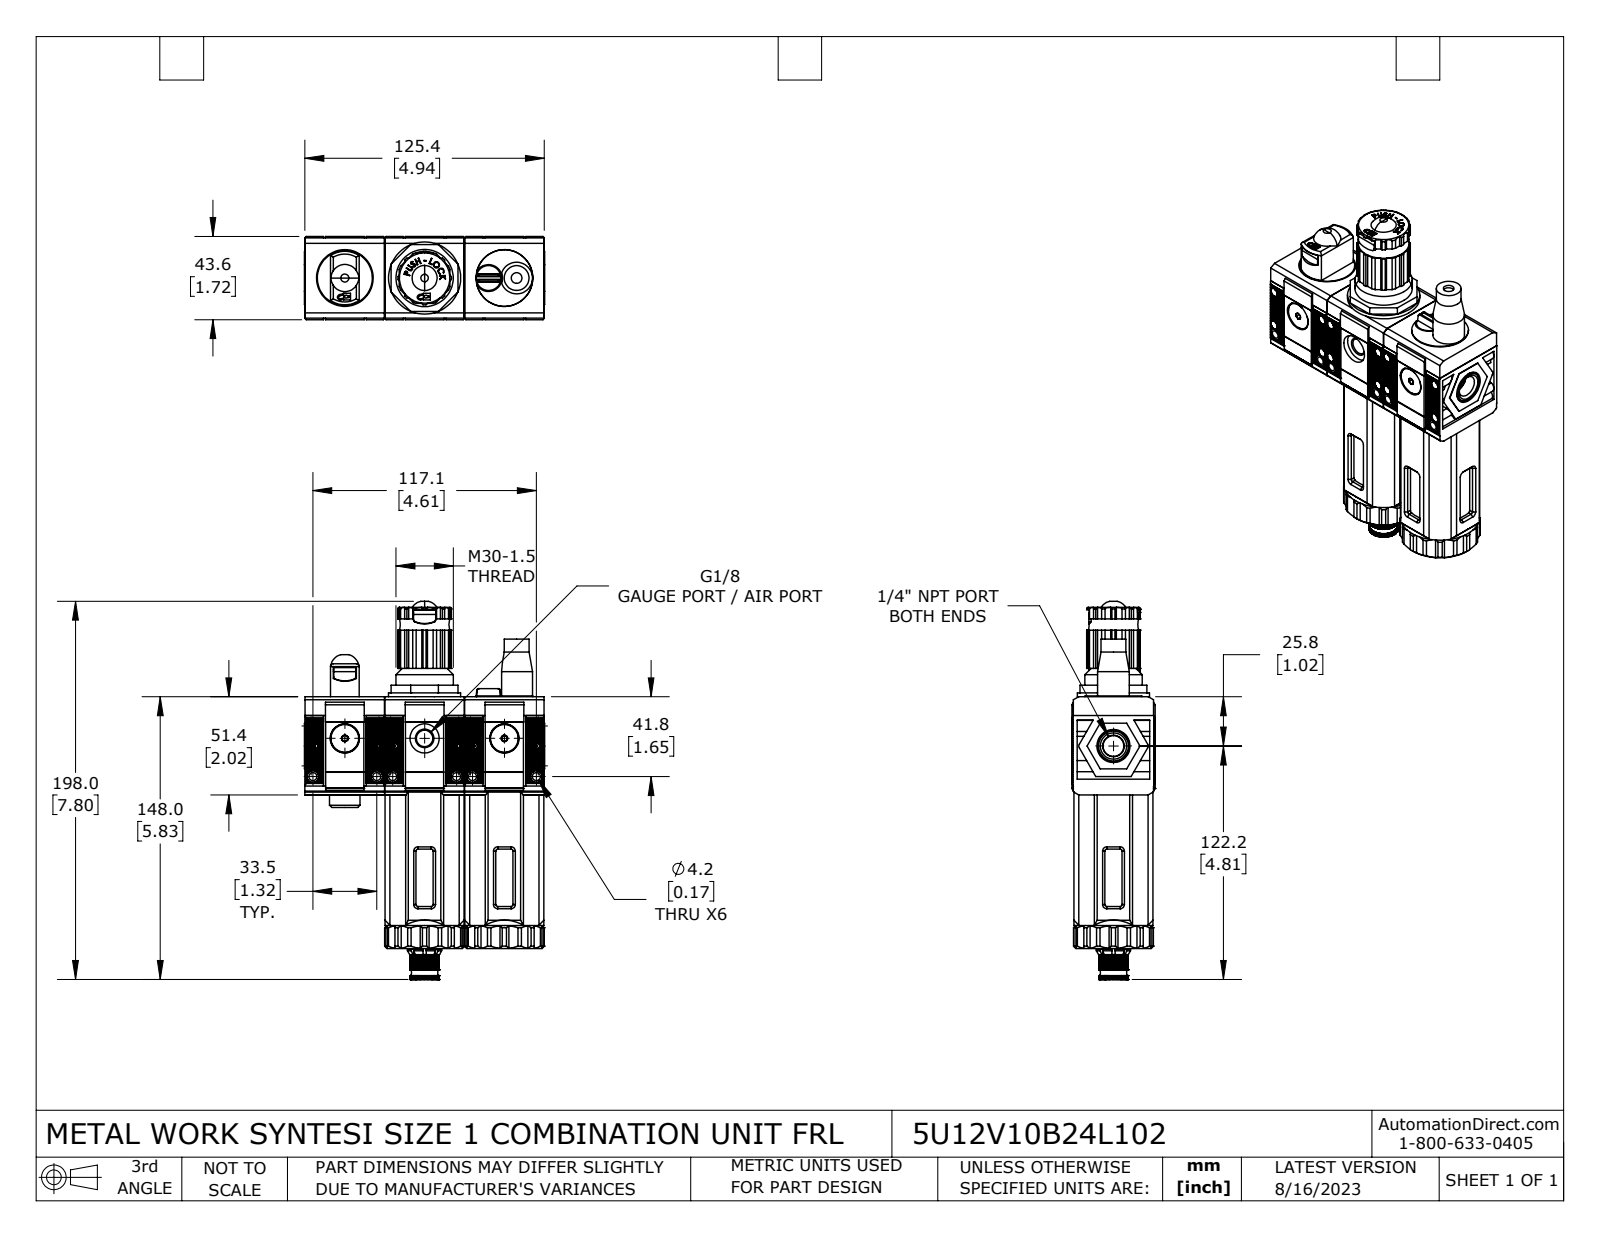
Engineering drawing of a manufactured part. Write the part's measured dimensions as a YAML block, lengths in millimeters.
part_name: "5U12V10B24L102"
step_written_by: "SolidWorks 2021 (CONFIG_CONTROL_DESIGN)"
units: millimeters
bodies: {solids: 40, faces: 4635, planar: 3330, cylindrical: 890, other: 415}
overall_size: [198, 125.8, 43.6]
volume: 388900
surface_area: 172600
round_holes:
  - {diameter: 2.1, count: 12}
  - {diameter: 3, count: 12}
  - {diameter: 4.7, count: 12}
  - {diameter: 4.2, count: 6}
  - {diameter: 8.6, count: 4}
  - {diameter: 15.3, count: 3}
  - {diameter: 3.5, count: 2}
  - {diameter: 29.7, count: 2}
  - {diameter: 30, count: 2}
  - {diameter: 31.3, count: 2}
  - {diameter: 34, count: 2}
  - {diameter: 35.4, count: 2}
round_bosses_or_shafts:
  - {diameter: 4.6, count: 12}
  - {diameter: 2.6, count: 12}
  - {diameter: 6.2, count: 6}
  - {diameter: 15, count: 3}
  - {diameter: 9.7, count: 3}
  - {diameter: 41.4, count: 2}
  - {diameter: 35.6, count: 2}
  - {diameter: 25, count: 2}
partial_cylinders:
  - {radius: 1, count: 14}
  - {radius: 3.1, count: 12}
  - {radius: 1.5, count: 7}
  - {radius: 0.6, count: 4}
  - {radius: 0.2, count: 2}
  - {radius: 0.5, count: 2}
  - {radius: 0.8, count: 2}
  - {radius: 1.3, count: 2}
face_to_face_distances: [41.8, 41.6, 41.7, 1.1, 42.5, 41.4, 34, 83.6, 7.8, 42]
hole_center_spacings: [41.8, 46.7, 83.6, 5.6, 18.8, 20.9, 22.9, 26.1]
